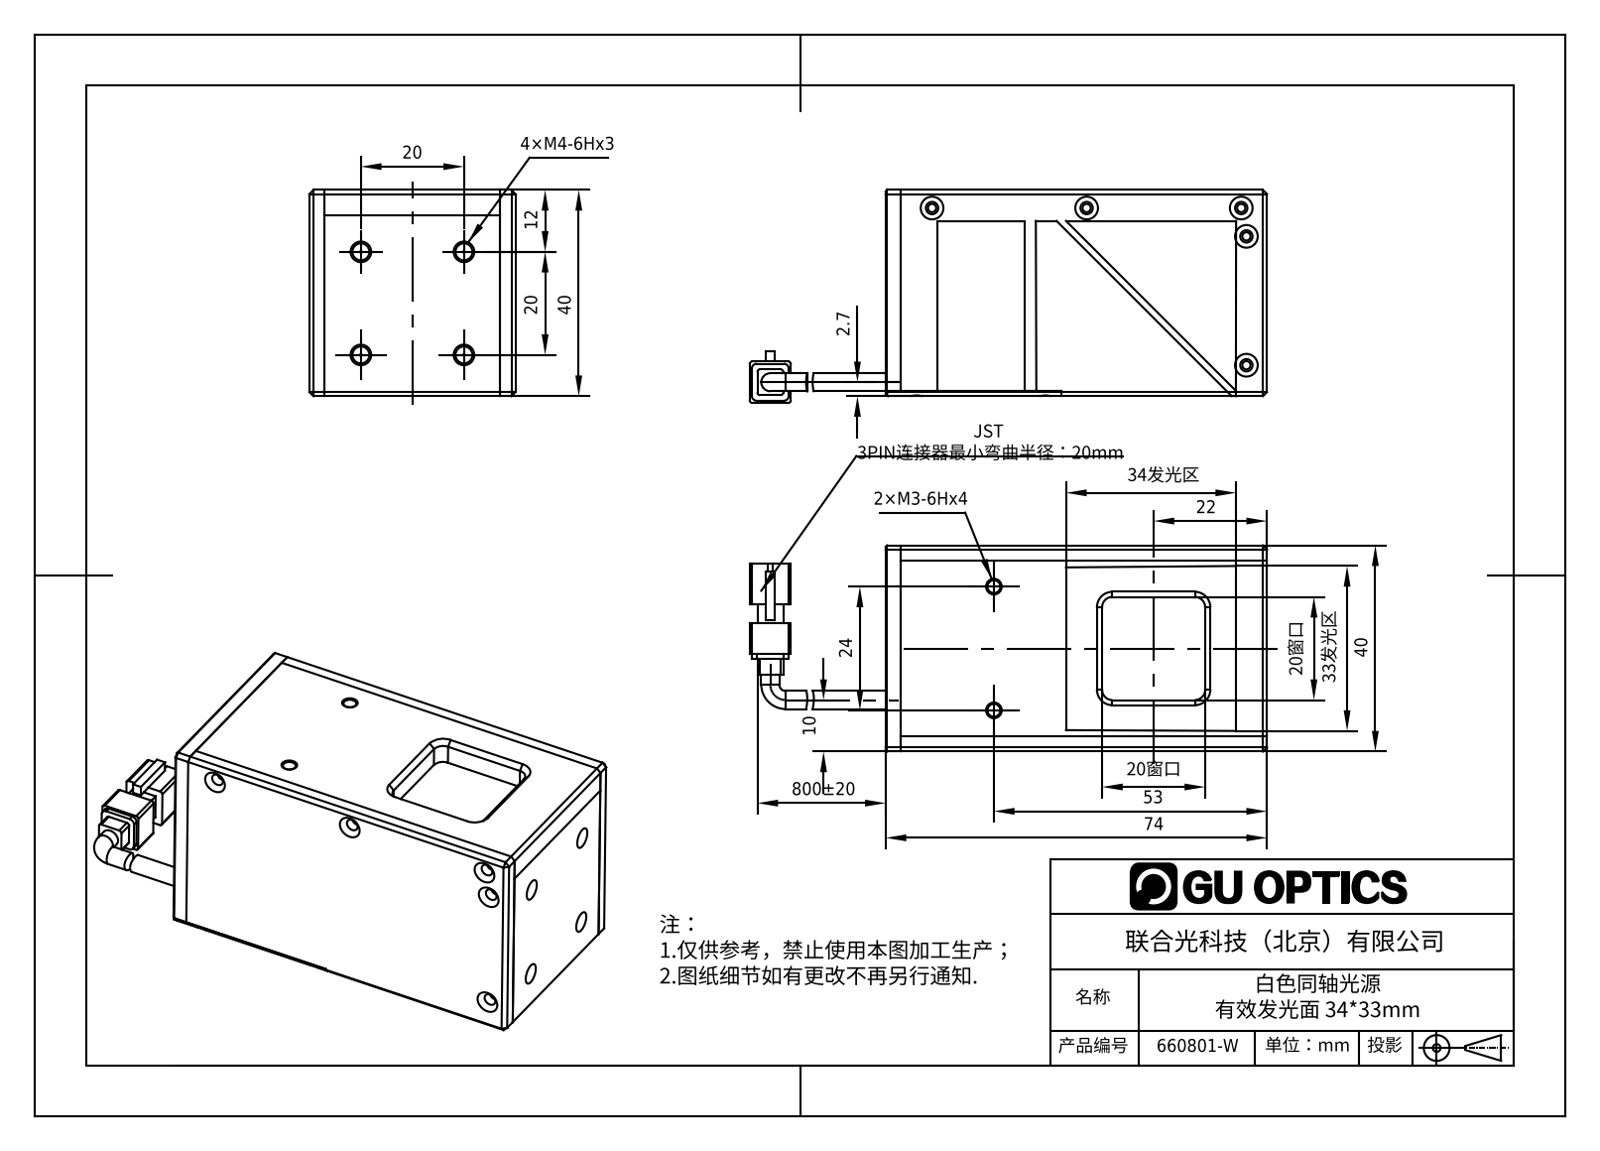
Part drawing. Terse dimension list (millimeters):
name: 白色同轴光源 有效发光面 3433mm
written by: SolidWorks 2016 (AUTOMOTIVE_DESIGN)
unit: mm
bodies: 10 solids, 784 faces (471 planar, 153 cylindrical, 160 other)
size: 100.39 × 41.3 × 40
volume: 48 647 mm³; area: 36 045 mm²
holes: 13× ⌀1.6, 13× ⌀2.4, 8× ⌀4, 6× ⌀2, 4× ⌀3.3, 2× ⌀2.5
bosses: 2× ⌀3.5
rounds: 8× R0.5, 6× R0.75, 5× R2, 4× R1, 4× R1.5, 3× R1.6, 1× R4
face distances: 1, 40, 3, 4, 36, 33, 34, 37, 6, 32
hole spacings: 30, 20, 25, 35, 7.5, 8.38, 11.41, 15.98
